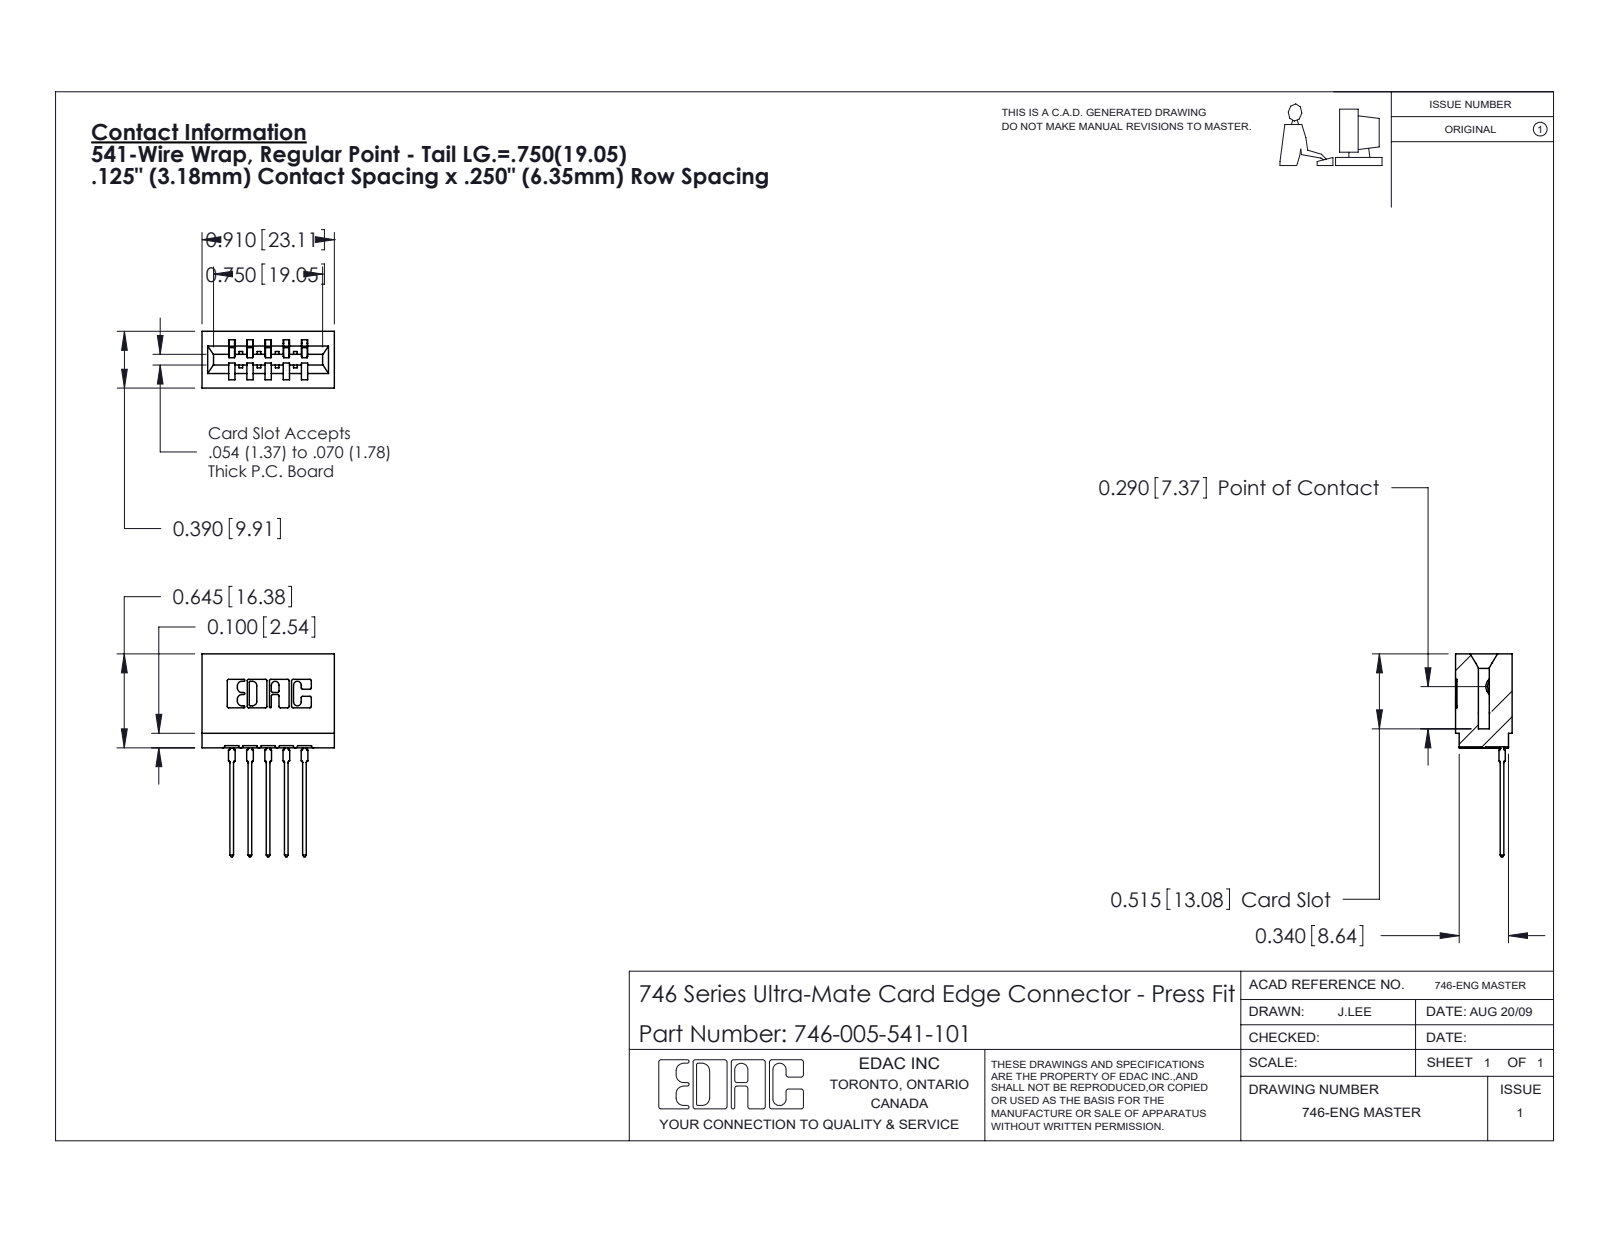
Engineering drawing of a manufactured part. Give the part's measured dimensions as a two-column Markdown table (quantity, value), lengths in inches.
| quantity | value |
| --- | --- |
| part name | 746-292-001_541; 746 Part_.515 Slot Depth - 01; 746-005-541-101 |
| STEP written by | SolidWorks 2020 (CONFIG_CONTROL_DESIGN) |
| units | inches |
| bodies | 6 solids, 637 faces (370 planar, 137 cylindrical, 130 other) |
| overall size | 1.394 × 0.91 × 0.39 |
| volume | 0.164 in³ |
| surface area | 5.404 in² |
| partial cylindrical surfaces (radius × count) | 0.01 × 22, 0.021 × 10, 0.007 × 6, 0.015 × 6, 0.031 × 6, 0.005 × 4, 0.011 × 4, 0.026 × 3 |
| main face-to-face distances | 0.25, 0.042, 0.333, 0.057, 0.125, 0.125, 0.39, 0.083, 0.208, 0.292 |
